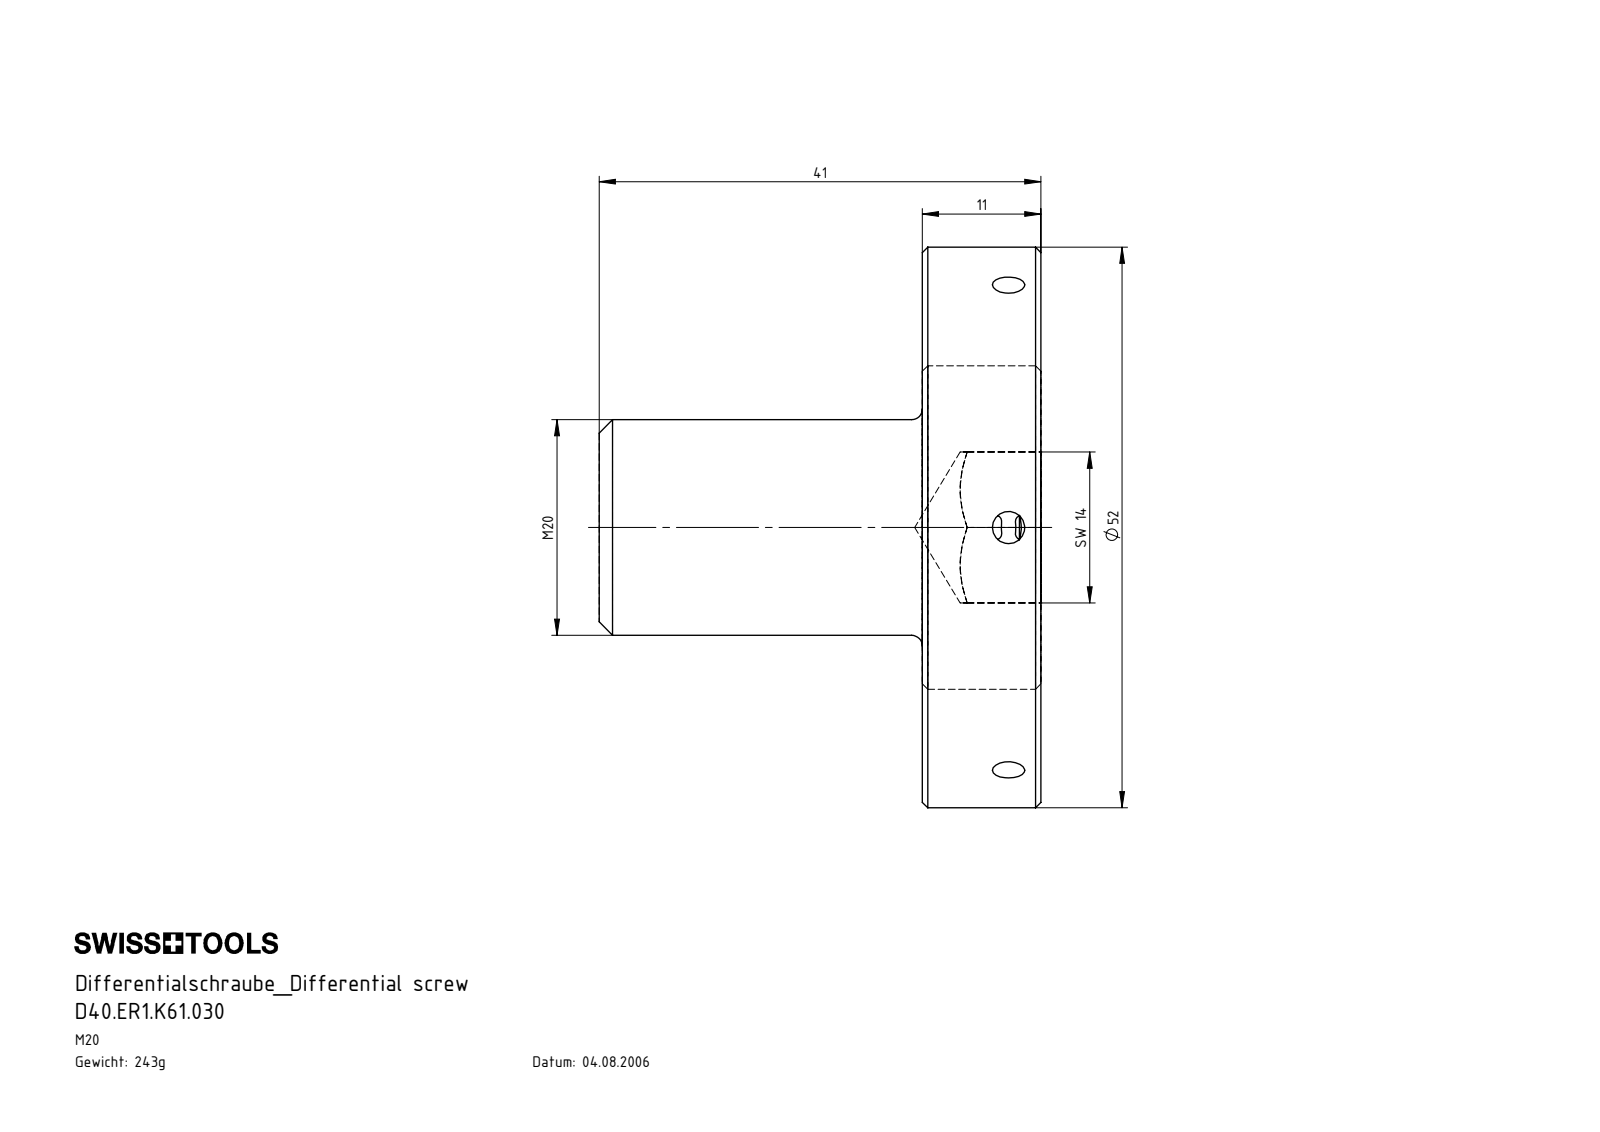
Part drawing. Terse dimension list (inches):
name: D40.ER1.K61.030; D40-ER1.K62.011_A; D40-ER1.K63.030_A
written by: SolidWorks 2017 (AUTOMOTIVE_DESIGN)
unit: in
bodies: 2 solids, 145 faces (11 planar, 78 cylindrical, 56 other)
size: 2.047 × 2.047 × 1.614
volume: 1.892 in³; area: 17.04 in²
holes: 9× ⌀0.118, 1× ⌀1.142
bosses: 1× ⌀2.047, 1× ⌀1.181, 1× ⌀0.787
face distances: 0.433, 1.181, 1.614, 0.551
hole spacings: 0.709, 1.228, 1.417
